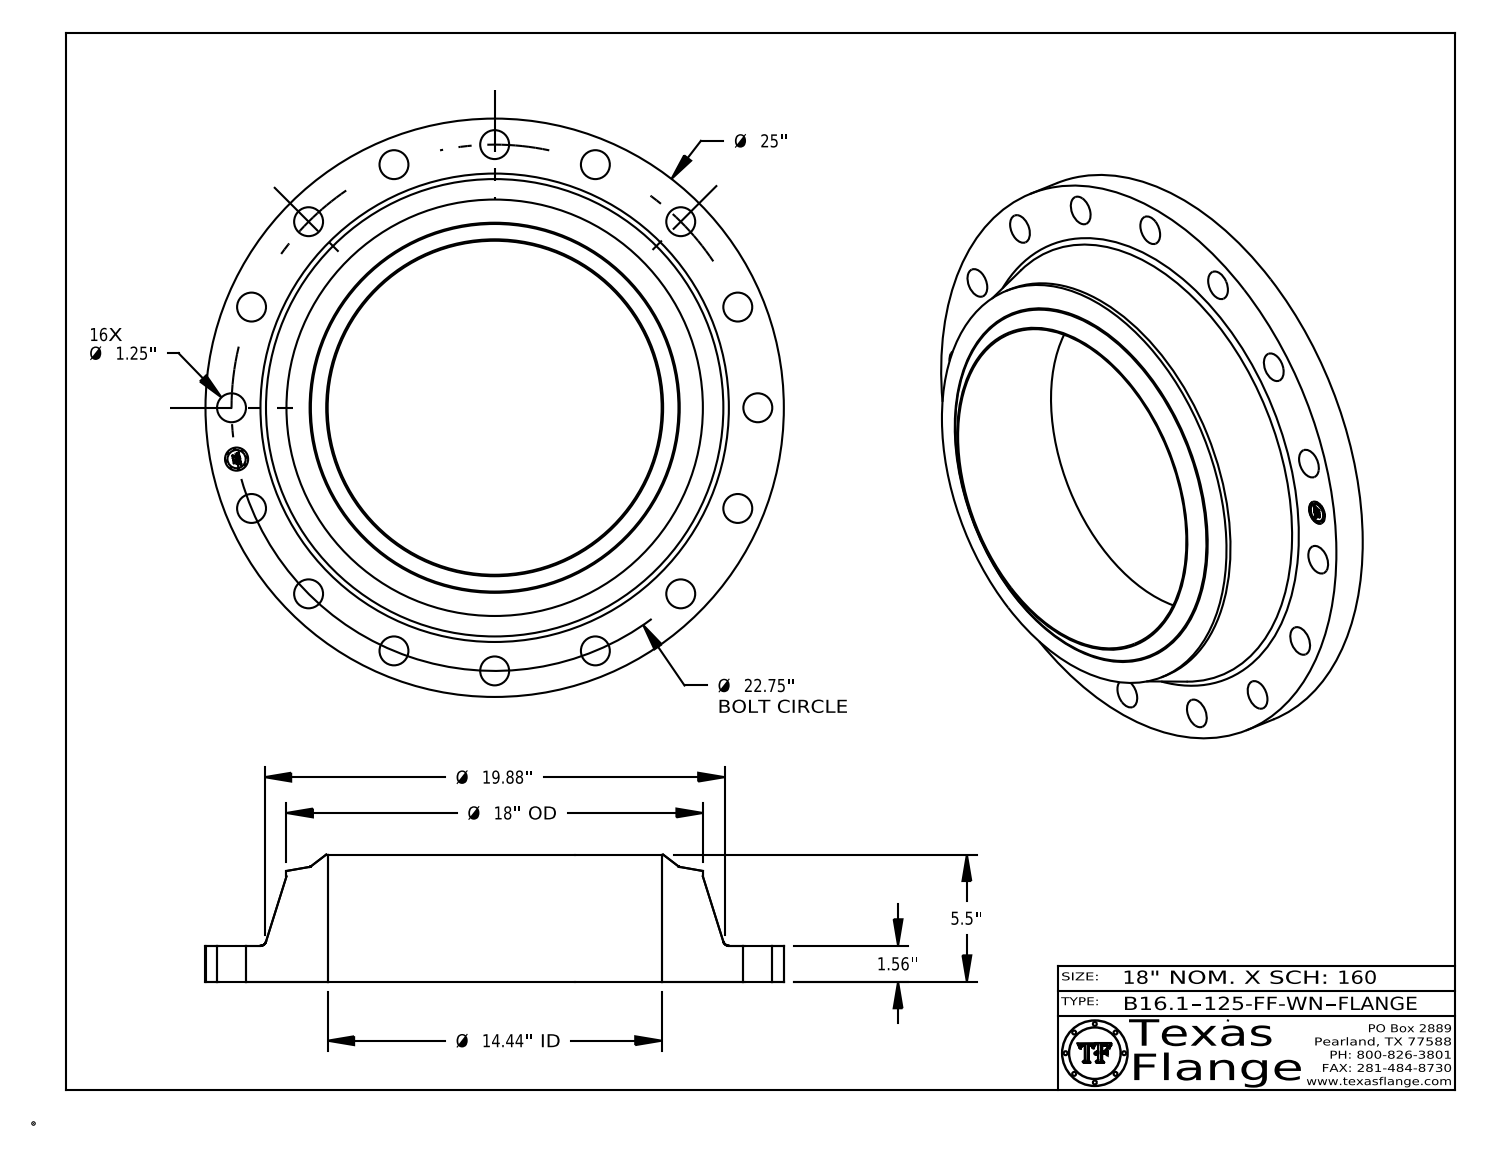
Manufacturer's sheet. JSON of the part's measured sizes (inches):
{"part_name": "B16.1, Class 125-FF-WN", "step_written_by": "CATIA V5 STEP AP214 (AUTOMOTIVE_DESIGN)", "units": "inches", "bodies": {"solids": 1, "faces": 436, "planar": 368, "cylindrical": 58, "other": 10}, "overall_size": [25, 25, 5.5], "volume_in3": 877.1, "surface_area_in2": 1236, "round_holes": [[1.25, 16], [1, 1], [14.438, 1]], "round_bosses_or_shafts": [[0.061, 8], [25, 1], [18, 1], [0.788, 1]], "face_to_face_distances": [1.56, 5.5, 3.94, 1.545, 0.015, 3.955, 0.298, 0.293, 0.054, 0.193], "hole_center_spacings": [12.639, 22.313, 11.375, 8.706, 16.087, 21.019, 4.438, 4.439]}
